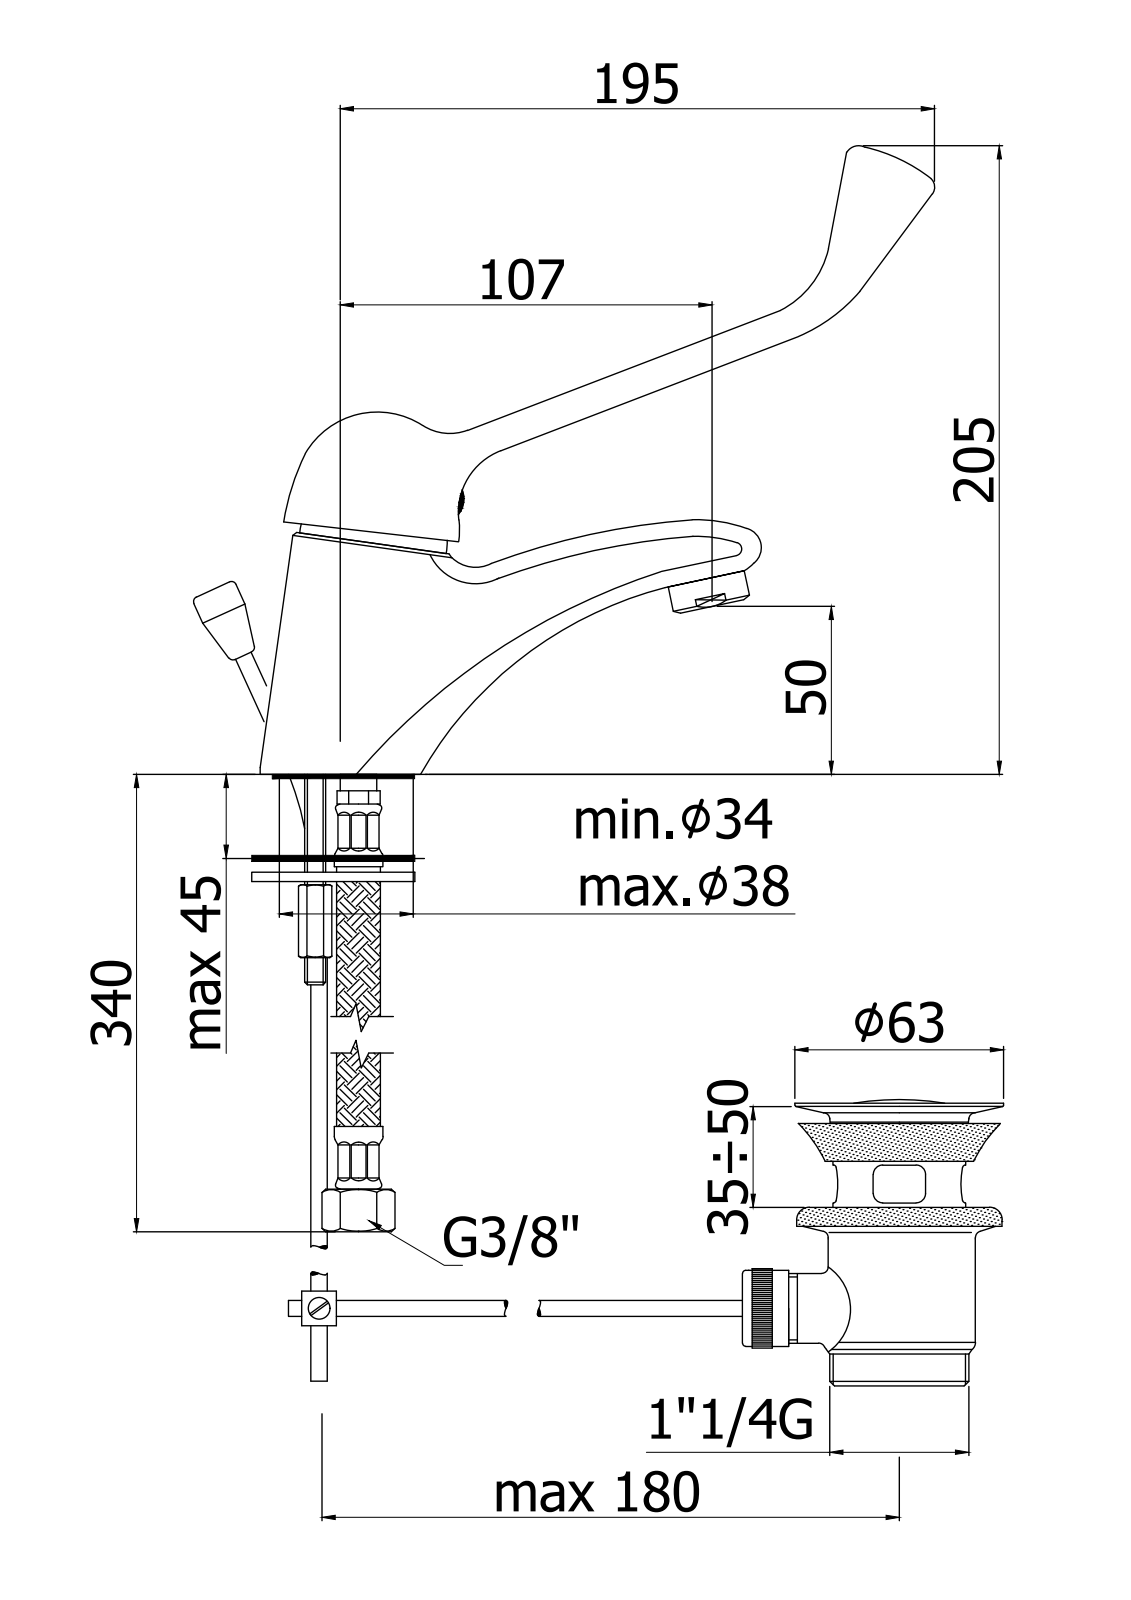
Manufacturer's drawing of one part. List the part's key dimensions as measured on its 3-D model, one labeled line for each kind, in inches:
Part name (STEP PRODUCT): ND305CR
STEP written by: CREO PARAMETRIC BY PTC INC, 2020044 (CONFIG_CONTROL_DESIGN)
Units: inches
Bodies: 1 solid, 194 faces (50 planar, 59 cylindrical, 85 other)
Overall size (bounding box): 8.98 × 8.78 × 2.067
Volume: 12.67 in³ · Surface area: 88.7 in²
Round holes (diameter × count): ⌀0.197 ×4, ⌀0.217 ×2, ⌀0.276 ×2, ⌀0.354 ×2, ⌀0.433 ×2, ⌀1.594 ×2, ⌀0.236 ×1, ⌀0.965 ×1, ⌀1.539 ×1, ⌀1.673 ×1
Round bosses / shafts (diameter × count): ⌀1.476 ×1, ⌀0.945 ×1, ⌀0.394 ×1, ⌀0.315 ×1, ⌀0.157 ×1
Partial cylindrical surfaces — rounded edges, fillets, slot ends (radius × count): R0.118 ×2, R0.157 ×1
Main face-to-face distances: 0.236, 2.027, 2.401, 0.374, 0.189, 0.425, 0.315, 0.551, 0.079, 0.11
Hole centre spacings: 0.339, 0.615, 0.338, 0.452, 0.465, 0.53, 0.615, 0.622
